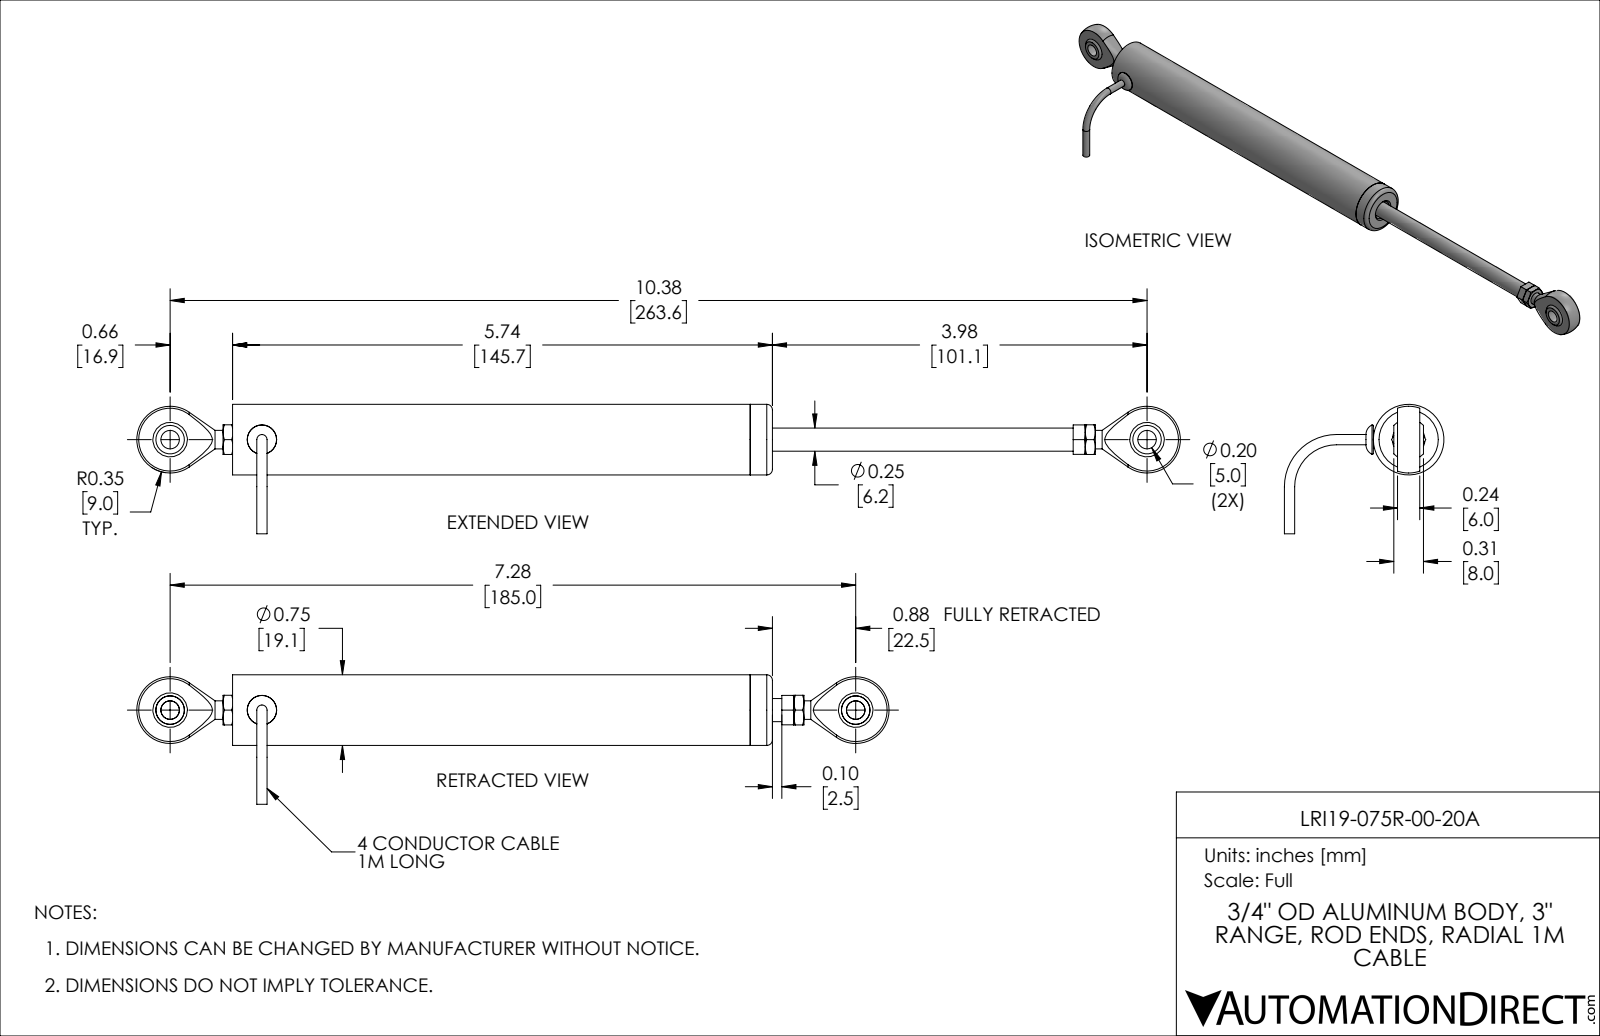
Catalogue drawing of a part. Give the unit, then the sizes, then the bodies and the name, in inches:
Units: inches
Overall size (bounding box): 7.995 × 1.695 × 1.375
Round holes (diameter × count): ⌀0.197 ×2, ⌀0.109 ×1, ⌀0.165 ×1, ⌀0.188 ×1, ⌀0.193 ×1, ⌀0.221 ×1, ⌀0.307 ×1, ⌀0.62 ×1, ⌀0.625 ×1, ⌀0.65 ×1, ⌀0.71 ×1, ⌀0.725 ×1
Round bosses / shafts (diameter × count): ⌀0.75 ×1, ⌀0.7 ×1, ⌀0.624 ×1, ⌀0.246 ×1, ⌀0.223 ×1, ⌀0.218 ×1, ⌀0.197 ×1, ⌀0.109 ×1
Main face-to-face distances: 0.236, 0.105, 5.626, 5.731, 5.495, 5.39, 0.236, 0.039, 0.276, 4.985
Hole centre spacings: 0.973, 6.313, 7.286
Volume: 1.229 in³ · Surface area: 40.33 in²
Bodies: 11 solids, 117 faces (42 planar, 30 cylindrical, 45 other)
Part name (STEP PRODUCT): LRI19-075R-00-20A
STEP written by: SolidWorks 2019 (AUTOMOTIVE_DESIGN)
